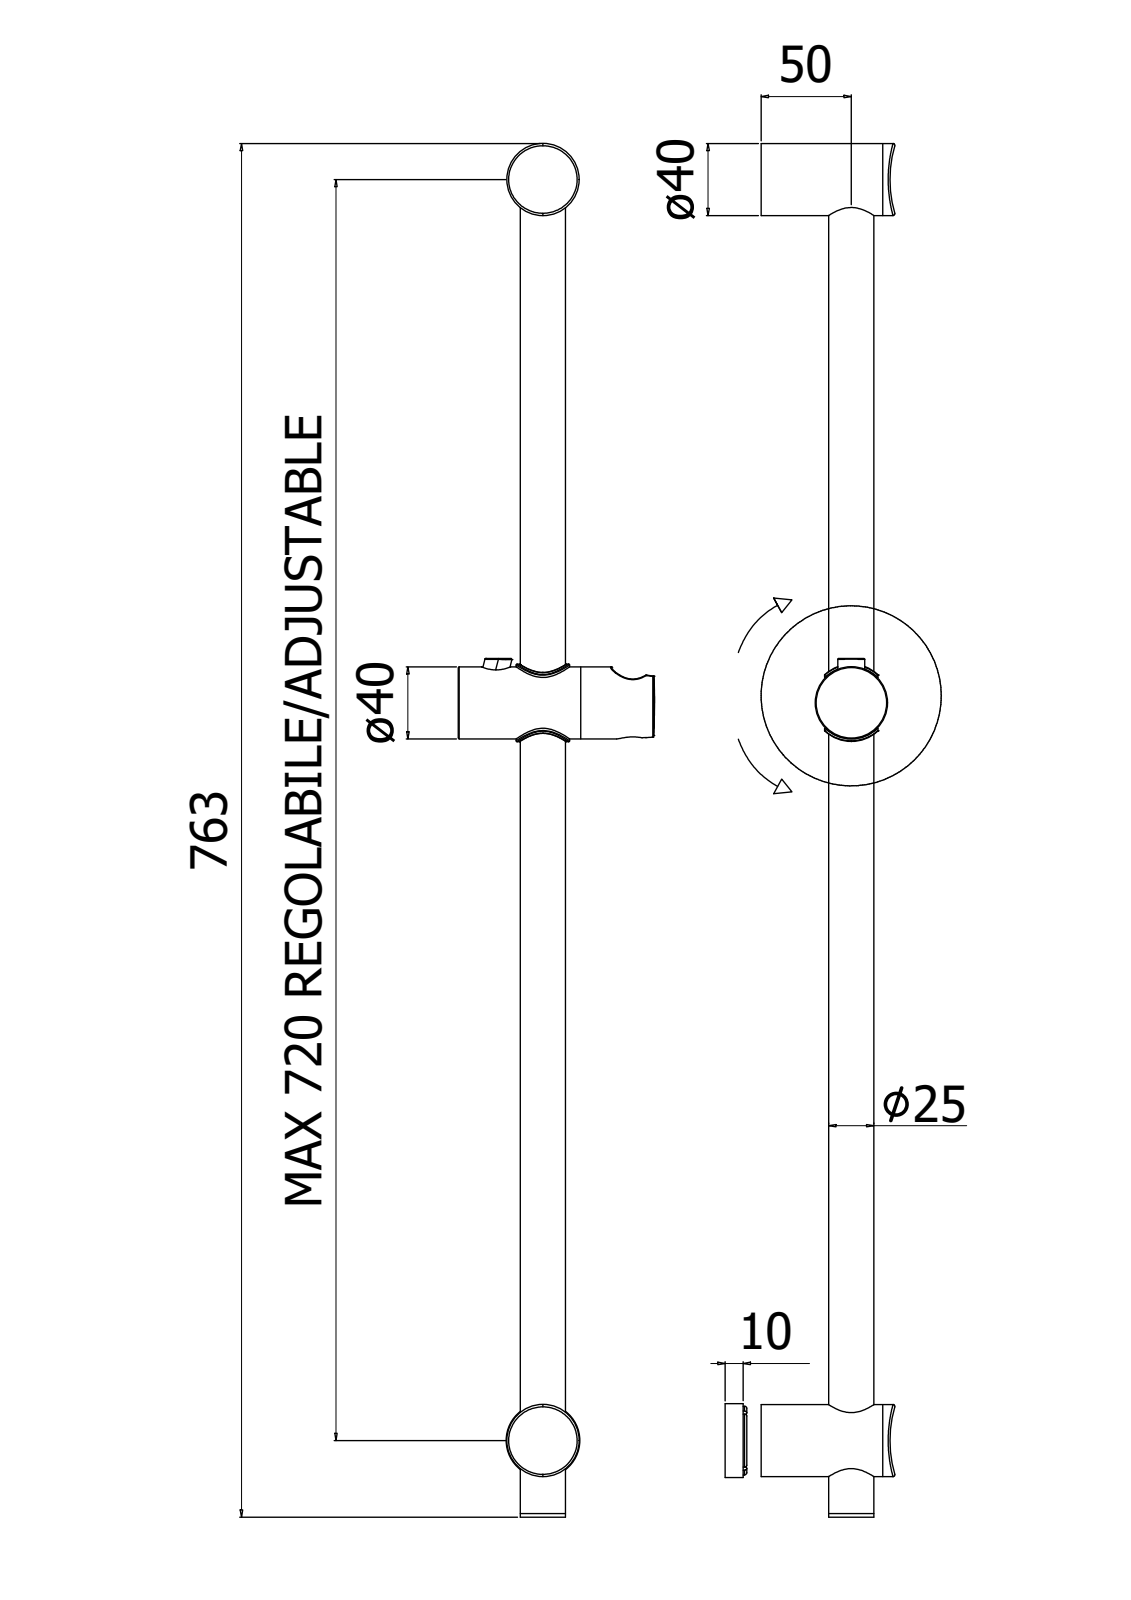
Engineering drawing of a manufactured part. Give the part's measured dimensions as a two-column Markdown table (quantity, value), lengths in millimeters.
| quantity | value |
| --- | --- |
| part name | ZSAL131CR |
| STEP written by | CREO PARAMETRIC BY PTC INC, 2020044 (CONFIG_CONTROL_DESIGN) |
| units | millimeters |
| bodies | 9 solids, 582 faces (173 planar, 258 cylindrical, 151 other) |
| overall size | 762.5 × 108.87 × 94.16 |
| volume | 122 545 mm³ |
| surface area | 203 947 mm² |
| round holes (diameter × count) | 4 × 4, 35 × 3, 11 × 2, 33 × 2, 5 × 1, 5.5 × 1, 6 × 1, 7 × 1, 10 × 1, 11.5 × 1, 16.2 × 1, 24 × 1 |
| round bosses / shafts (diameter × count) | 40 × 3, 41 × 1, 38.1 × 1, 29.6 × 1, 27.9 × 1, 25 × 1, 15 × 1, 10 × 1 |
| partial cylindrical surfaces (radius × count) | 0.2 × 114, 0.5 × 4, 21.5 × 3, 1.52 × 2, 2 × 2, 68.17 × 2, 70.17 × 2, 8 × 1 |
| main face-to-face distances | 2, 0.8, 401.4, 402.19, 0.79, 402.2, 10, 1, 401.39, 0.81 |
| hole center spacings | 13.5, 700, 27, 686.5, 713.5, 0.7, 12.8, 14.2 |
